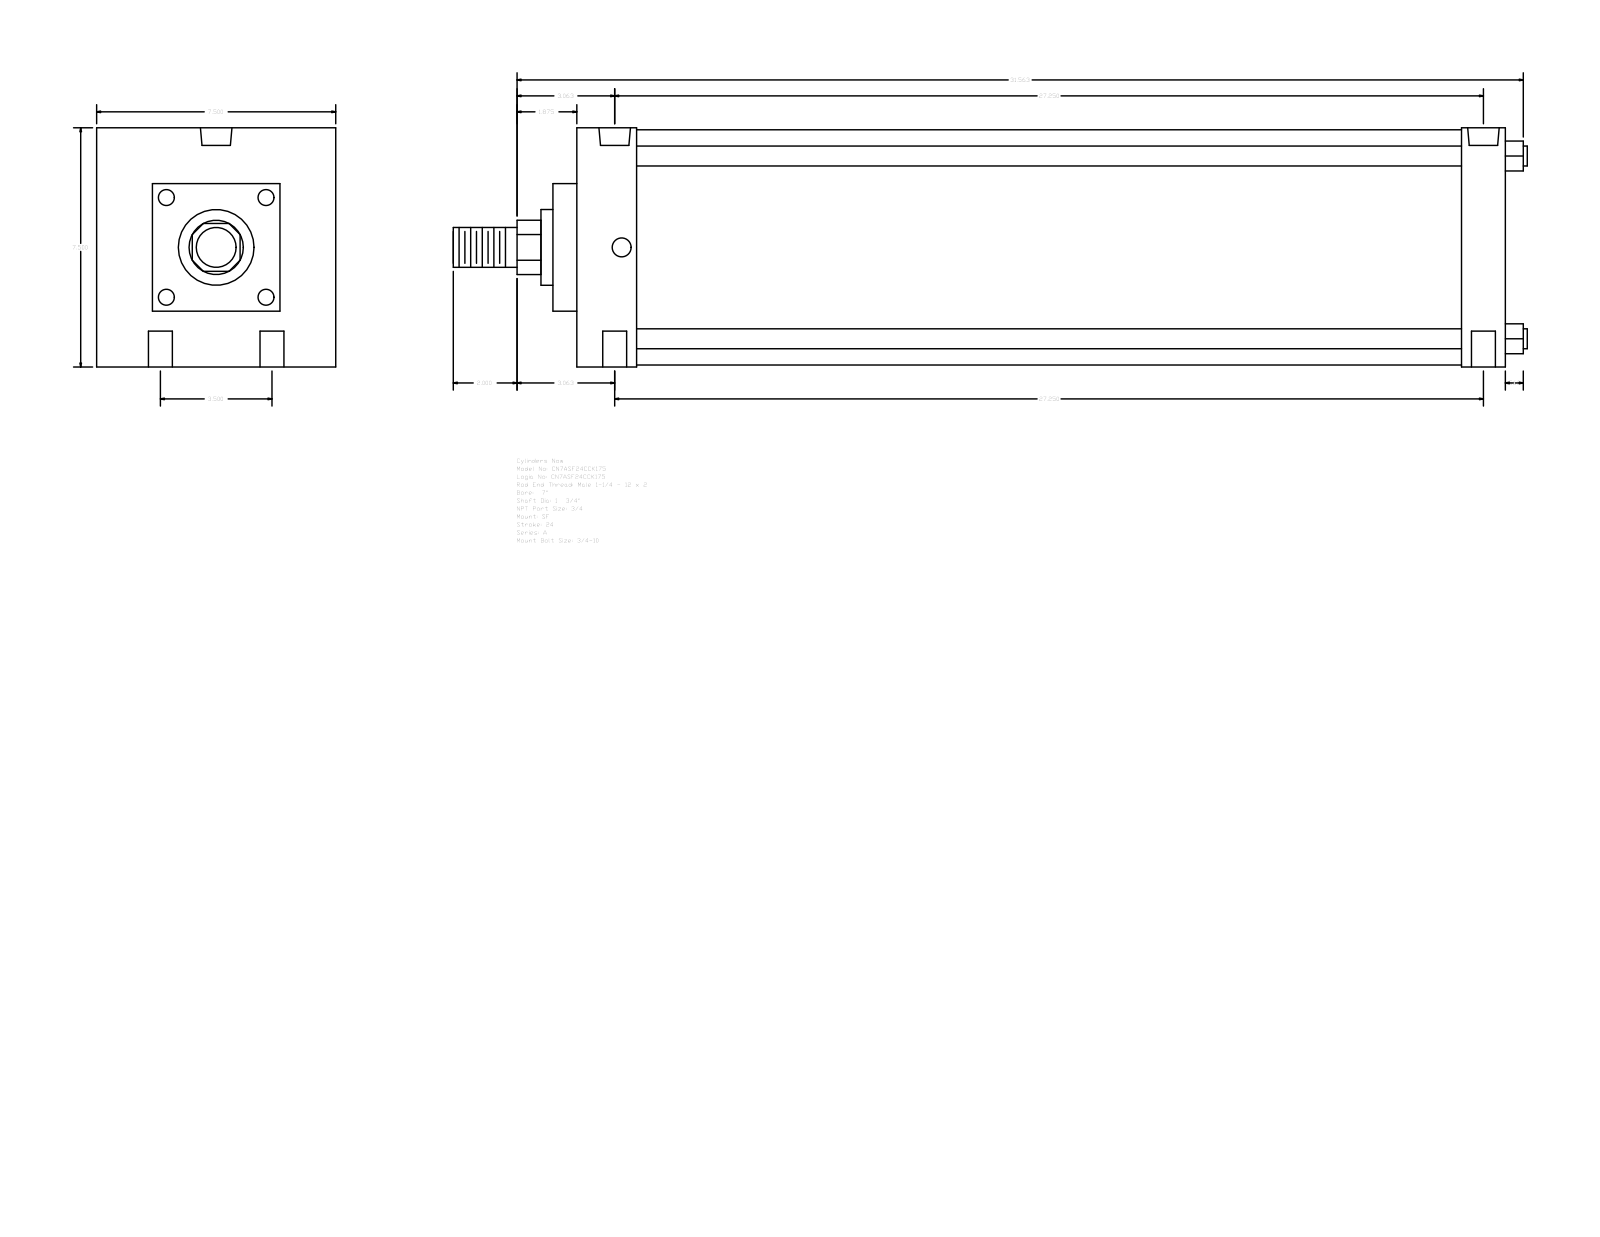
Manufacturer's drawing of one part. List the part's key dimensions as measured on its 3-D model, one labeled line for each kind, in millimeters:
Part name (STEP PRODUCT): A_SF__0700_1.75
STEP written by: GSSL Pune (CONFIG_CONTROL_DESIGN)
Units: millimetres
Bodies: 0 solids, 93 faces (67 planar, 26 cylindrical, 0 other)
Overall size (bounding box): 855.66 × 190.5 × 190.5
Round holes (diameter × count): ⌀19.05 ×4, ⌀15.08 ×2, ⌀25.12 ×2
Round bosses / shafts (diameter × count): ⌀15.88 ×4, ⌀187.32 ×1, ⌀60.33 ×1, ⌀44.45 ×1, ⌀31.75 ×1
Partial cylindrical surfaces — rounded edges, fillets, slot ends (radius × count): R21.63 ×1
Main face-to-face distances: 190.5, 739.78, 146.05, 19.05, 47.63, 704.86, 657.23, 692.15, 34.92, 44.45
Hole centre spacings: 44.45, 693.58, 692.15, 88.9, 697.84, 681.03
